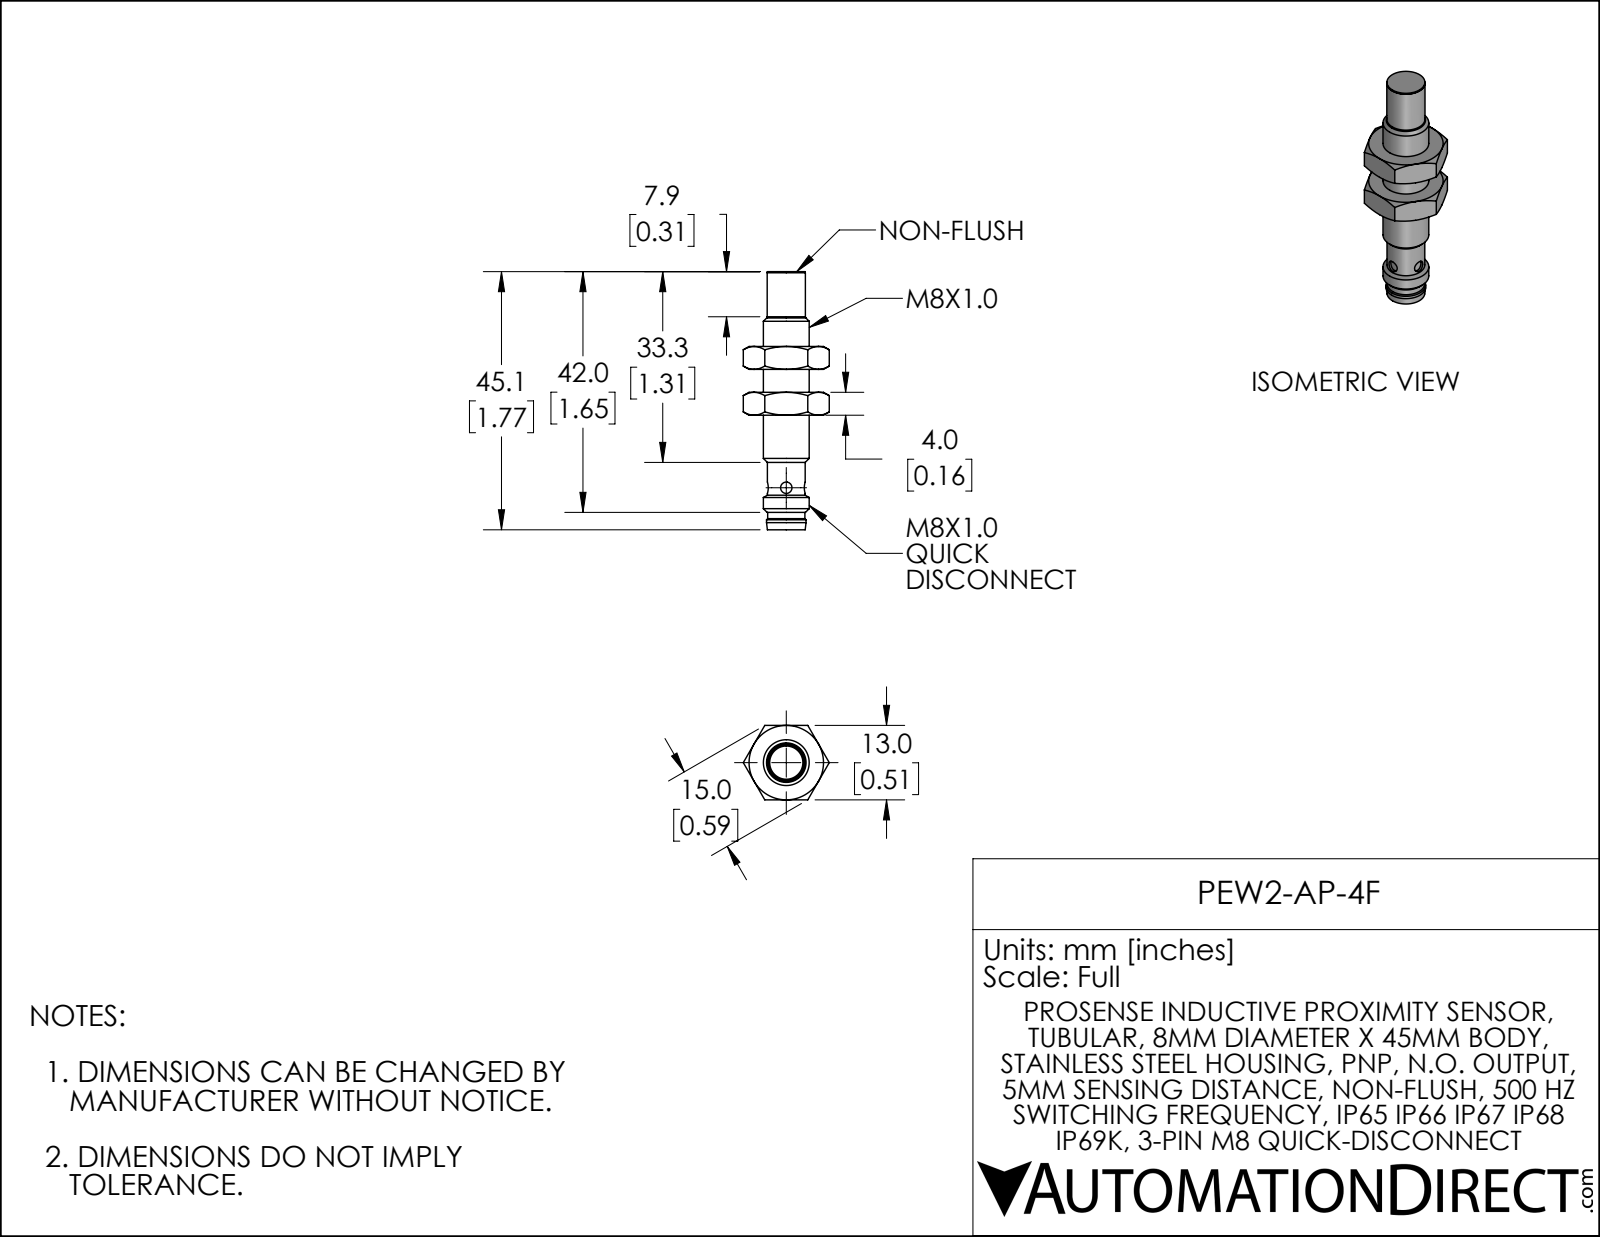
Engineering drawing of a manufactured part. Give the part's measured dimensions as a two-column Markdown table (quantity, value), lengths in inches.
| quantity | value |
| --- | --- |
| part name | PEW2-AP-4F |
| STEP written by | SolidWorks 2019 (CONFIG_CONTROL_DESIGN) |
| units | inches |
| bodies | 3 solids, 75 faces (21 planar, 18 cylindrical, 36 other) |
| overall size | 1.774 × 0.591 × 0.512 |
| volume | 0.164 in³ |
| surface area | 3.368 in² |
| round holes (diameter × count) | 0.079 × 2, 0.272 × 1 |
| round bosses / shafts (diameter × count) | 0.315 × 1, 0.272 × 1, 0.263 × 1, 0.261 × 1, 0.26 × 1, 0.256 × 1, 0.228 × 1 |
| main face-to-face distances | 0.157, 0.512, 0.315, 0.987, 0.829, 0.672, 0.589, 0.746, 0.904, 1.575 |
